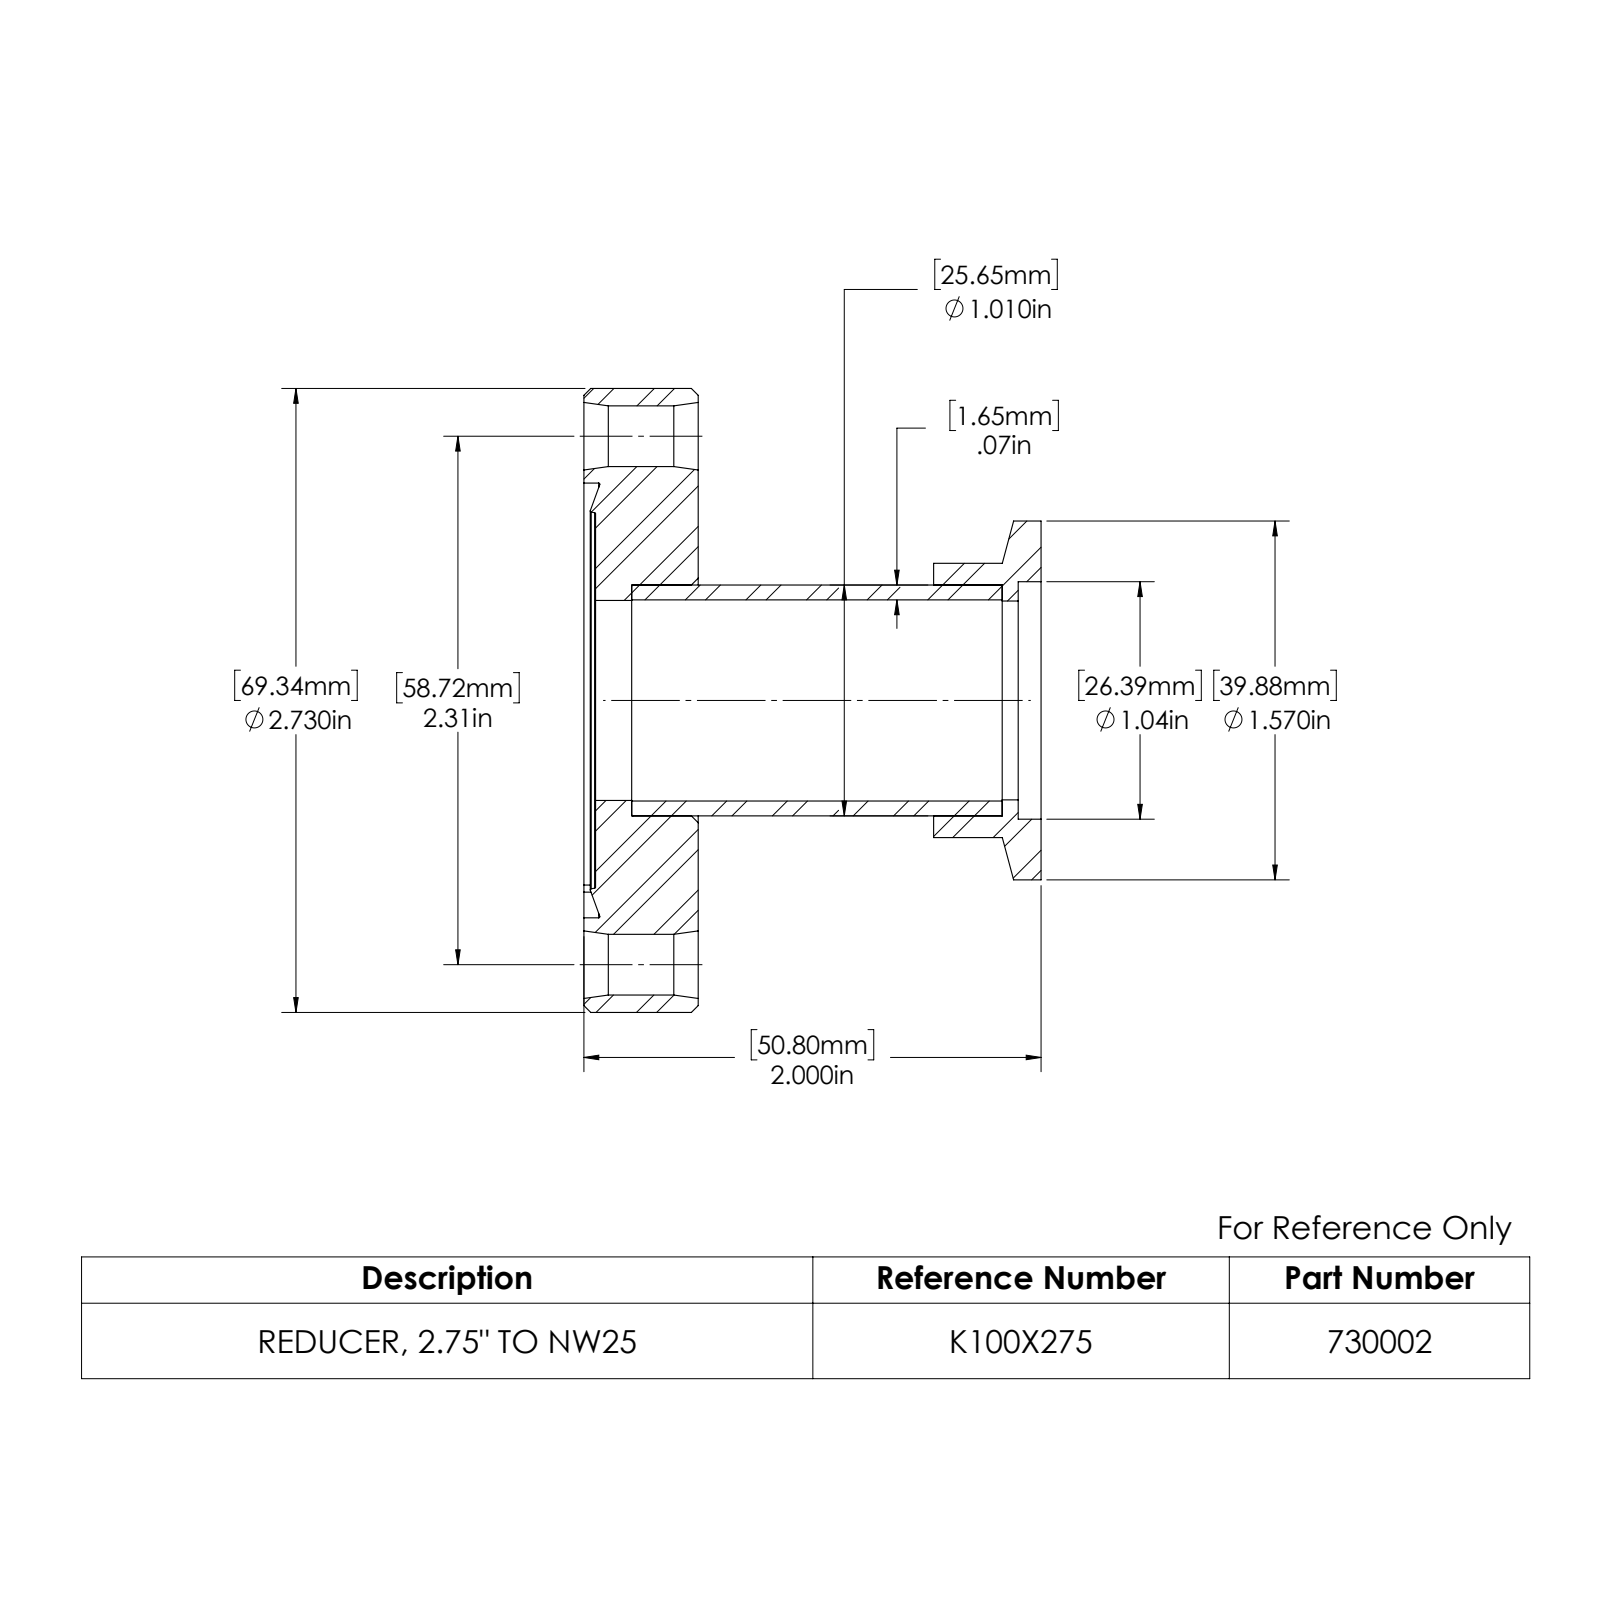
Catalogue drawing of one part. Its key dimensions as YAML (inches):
part_name: "110012; 713002; 730002; 940132"
step_written_by: "SolidWorks 2022 (AUTOMOTIVE_DESIGN)"
units: inches
bodies: {solids: 3, faces: 96, planar: 17, cylindrical: 34, other: 45}
overall_size: [2.73, 2.73, 2]
volume: 2.862
surface_area: 34.06
round_holes:
  - {diameter: 0.266, count: 6}
  - {diameter: 0.87, count: 1}
  - {diameter: 0.875, count: 1}
  - {diameter: 0.88, count: 1}
  - {diameter: 1.01, count: 1}
  - {diameter: 1.039, count: 1}
  - {diameter: 1.902, count: 1}
round_bosses_or_shafts:
  - {diameter: 2.73, count: 1}
  - {diameter: 1.57, count: 1}
  - {diameter: 1.2, count: 1}
face_to_face_distances: [0.5, 0.449, 0.051, 1.5, 1.949, 2, 0.17, 1.33, 1.779, 1.83]
hole_center_spacings: [1.156, 2.002, 1.156, 2.312]
